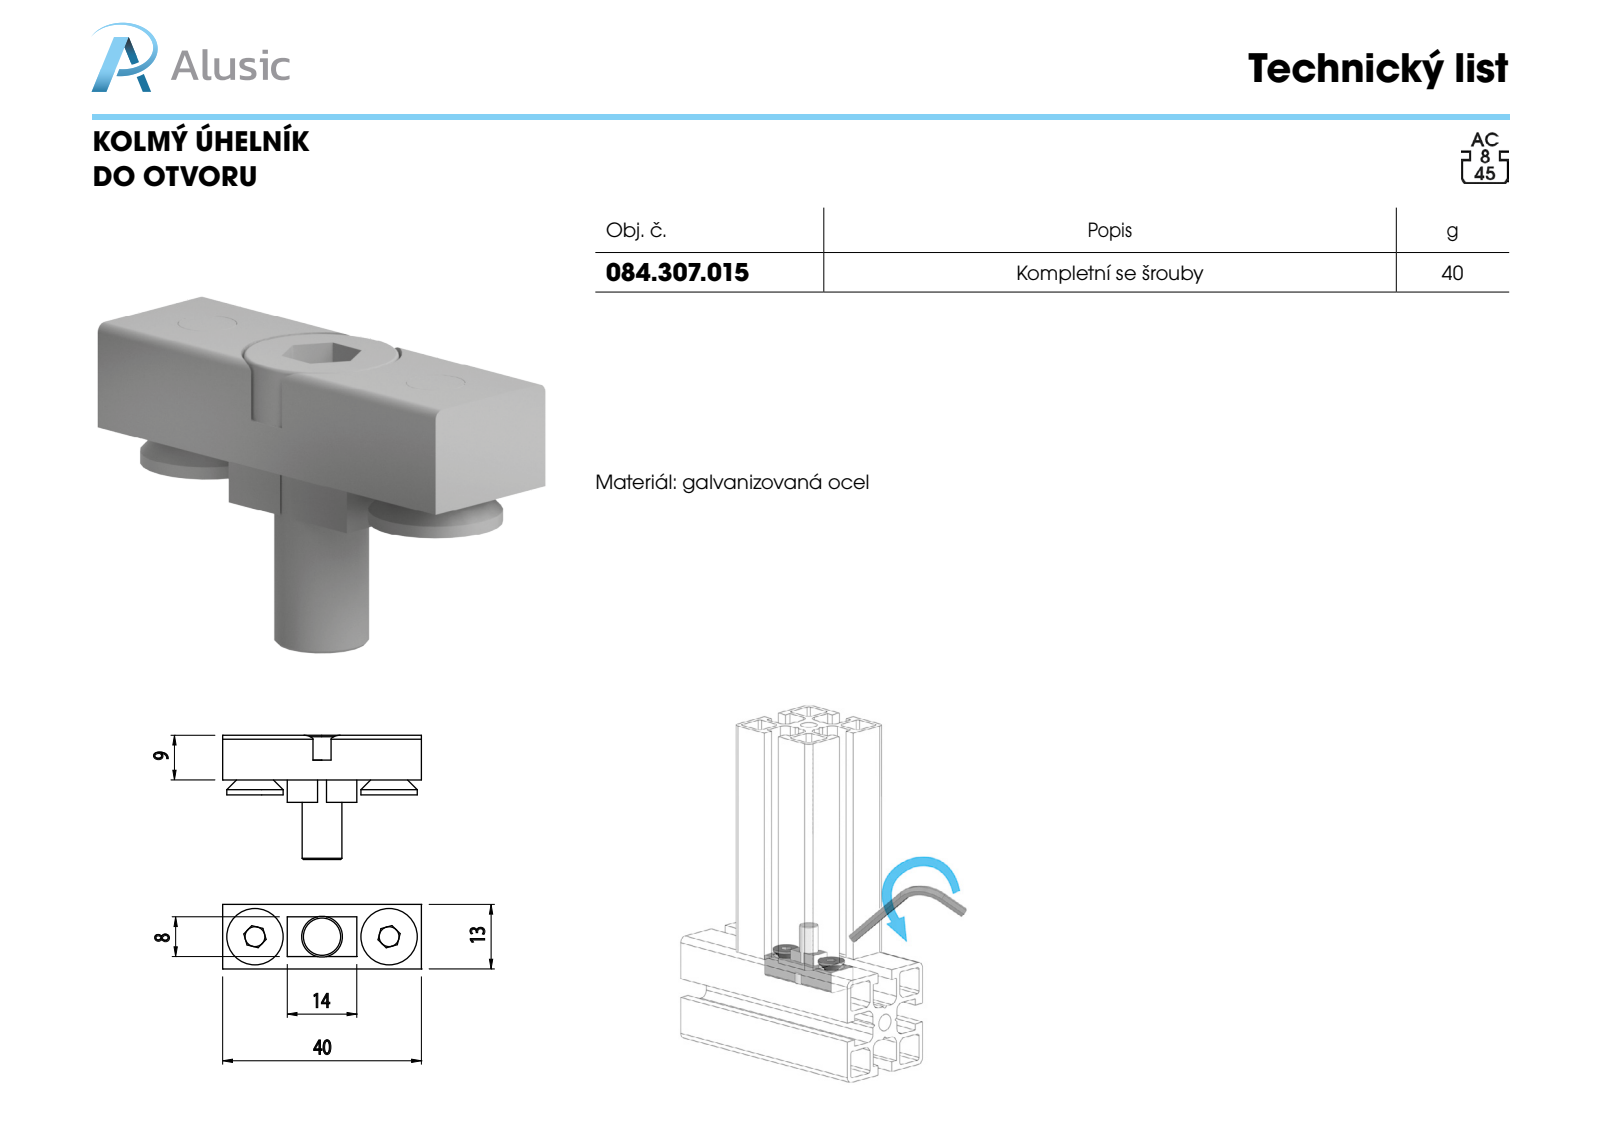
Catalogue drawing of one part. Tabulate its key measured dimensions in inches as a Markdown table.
| quantity | value |
| --- | --- |
| part name | 084.307.015 |
| STEP written by | SolidWorks 2011 (CONFIG_CONTROL_DESIGN) |
| units | inches |
| bodies | 1 solid, 32 faces (16 planar, 12 cylindrical, 4 other) |
| overall size | 1.575 × 0.531 × 0.512 |
| volume | 0.212 in³ |
| surface area | 3.962 in² |
| round holes (diameter × count) | 0.197 × 2, 0.323 × 1, 0.531 × 1 |
| partial cylindrical surfaces (radius × count) | 0.031 × 2 |
| main face-to-face distances | 0.512, 0.354, 1.575, 0.098, 0.413, 0.197, 0.157, 1.063, 0.531, 0.335 |
| hole center spacings | 0.531, 1.063 |
